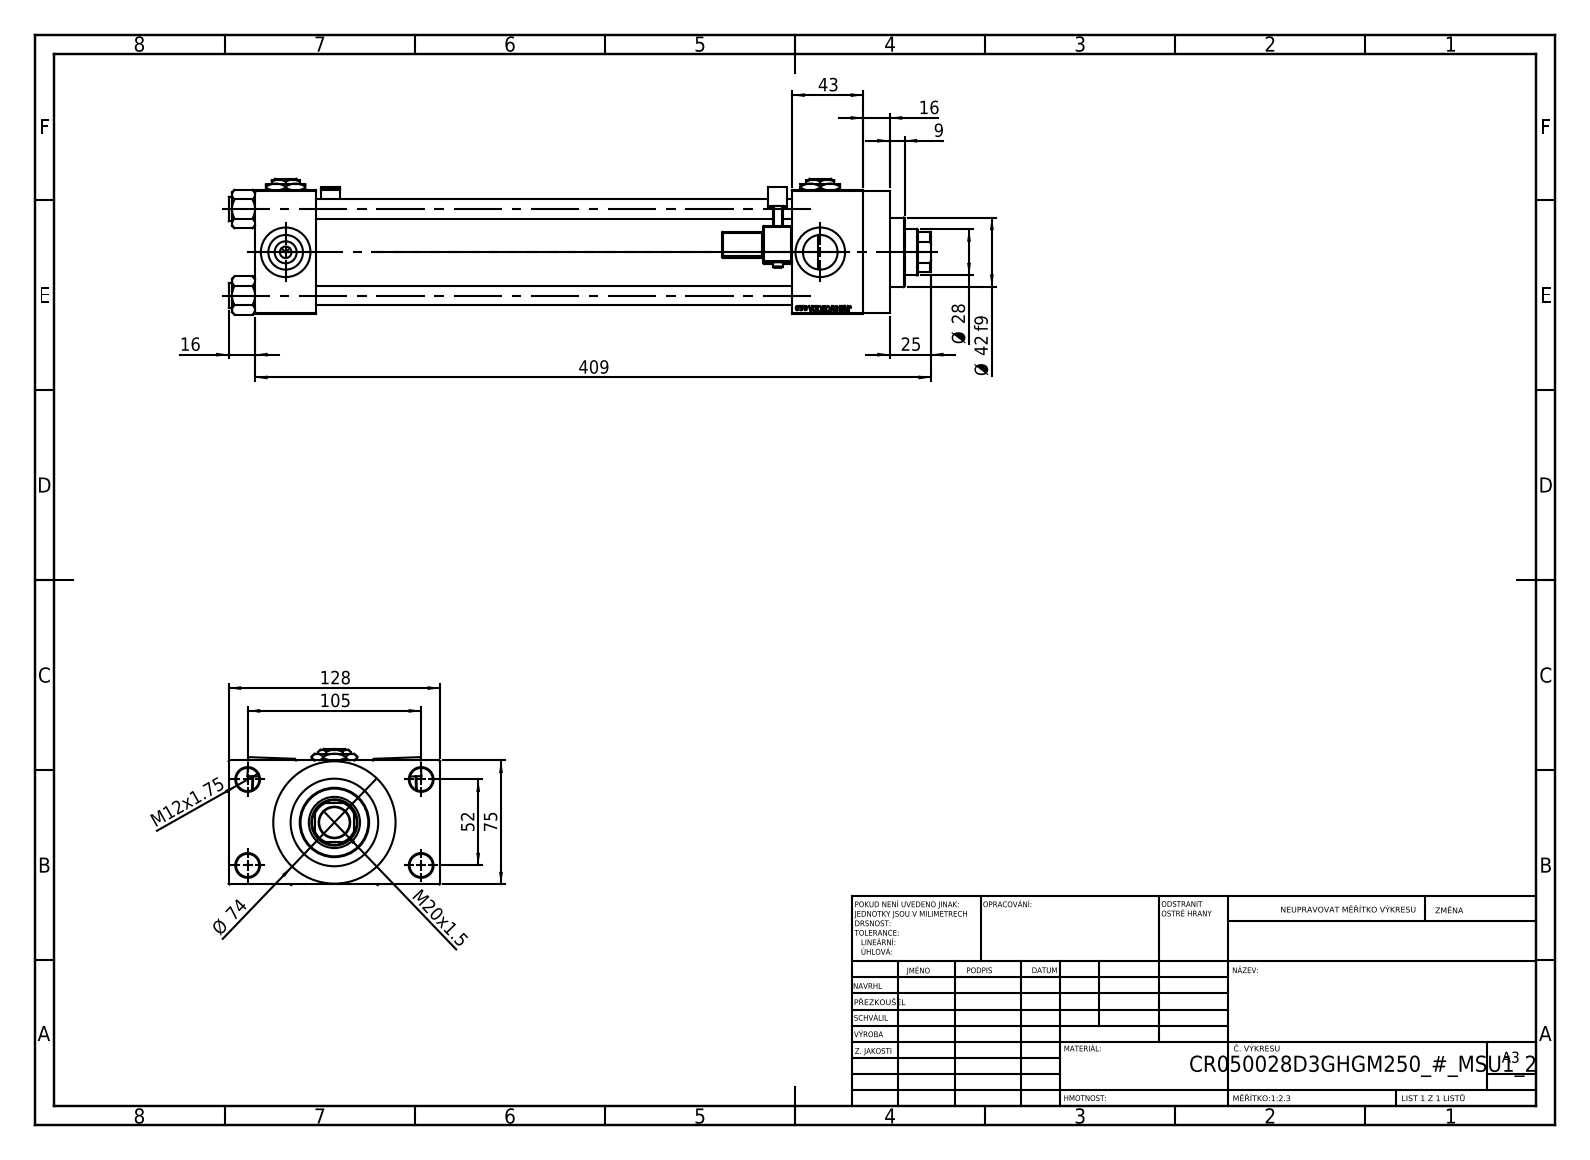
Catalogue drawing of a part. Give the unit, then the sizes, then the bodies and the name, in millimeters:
Units: millimetres
Overall size (bounding box): 425 × 128 × 82.27
Round holes (diameter × count): ⌀12 ×4, ⌀14 ×4, ⌀20.96 ×4, ⌀30 ×4, ⌀7 ×3, ⌀18.5 ×1, ⌀28 ×1, ⌀31 ×1, ⌀41 ×1, ⌀50 ×1, ⌀53 ×1
Round bosses / shafts (diameter × count): ⌀15 ×4, ⌀6 ×2, ⌀74 ×1, ⌀56 ×1, ⌀42 ×1
Partial cylindrical surfaces — rounded edges, fillets, slot ends (radius × count): R0.5 ×48, R1 ×2, R2.5 ×2, R4 ×2, R13.5 ×1
Main face-to-face distances: 75, 288, 37, 325, 26.5, 101.5, 368, 331, 43, 16
Hole centre spacings: 26.35, 36.98, 52.3, 58.43, 58.59, 78.65, 94.37, 52
Volume: 1 204 000 mm³ · Surface area: 318 618 mm²
Bodies: 15 solids, 1358 faces (603 planar, 159 cylindrical, 596 other)
Part name (STEP PRODUCT): V215CR_MSU; V215CR_D_TYCINKA; NUT_M5_D; V215CR_D_Body (+3 more)
STEP written by: SolidWorks 2019 (CONFIG_CONTROL_DESIGN)
